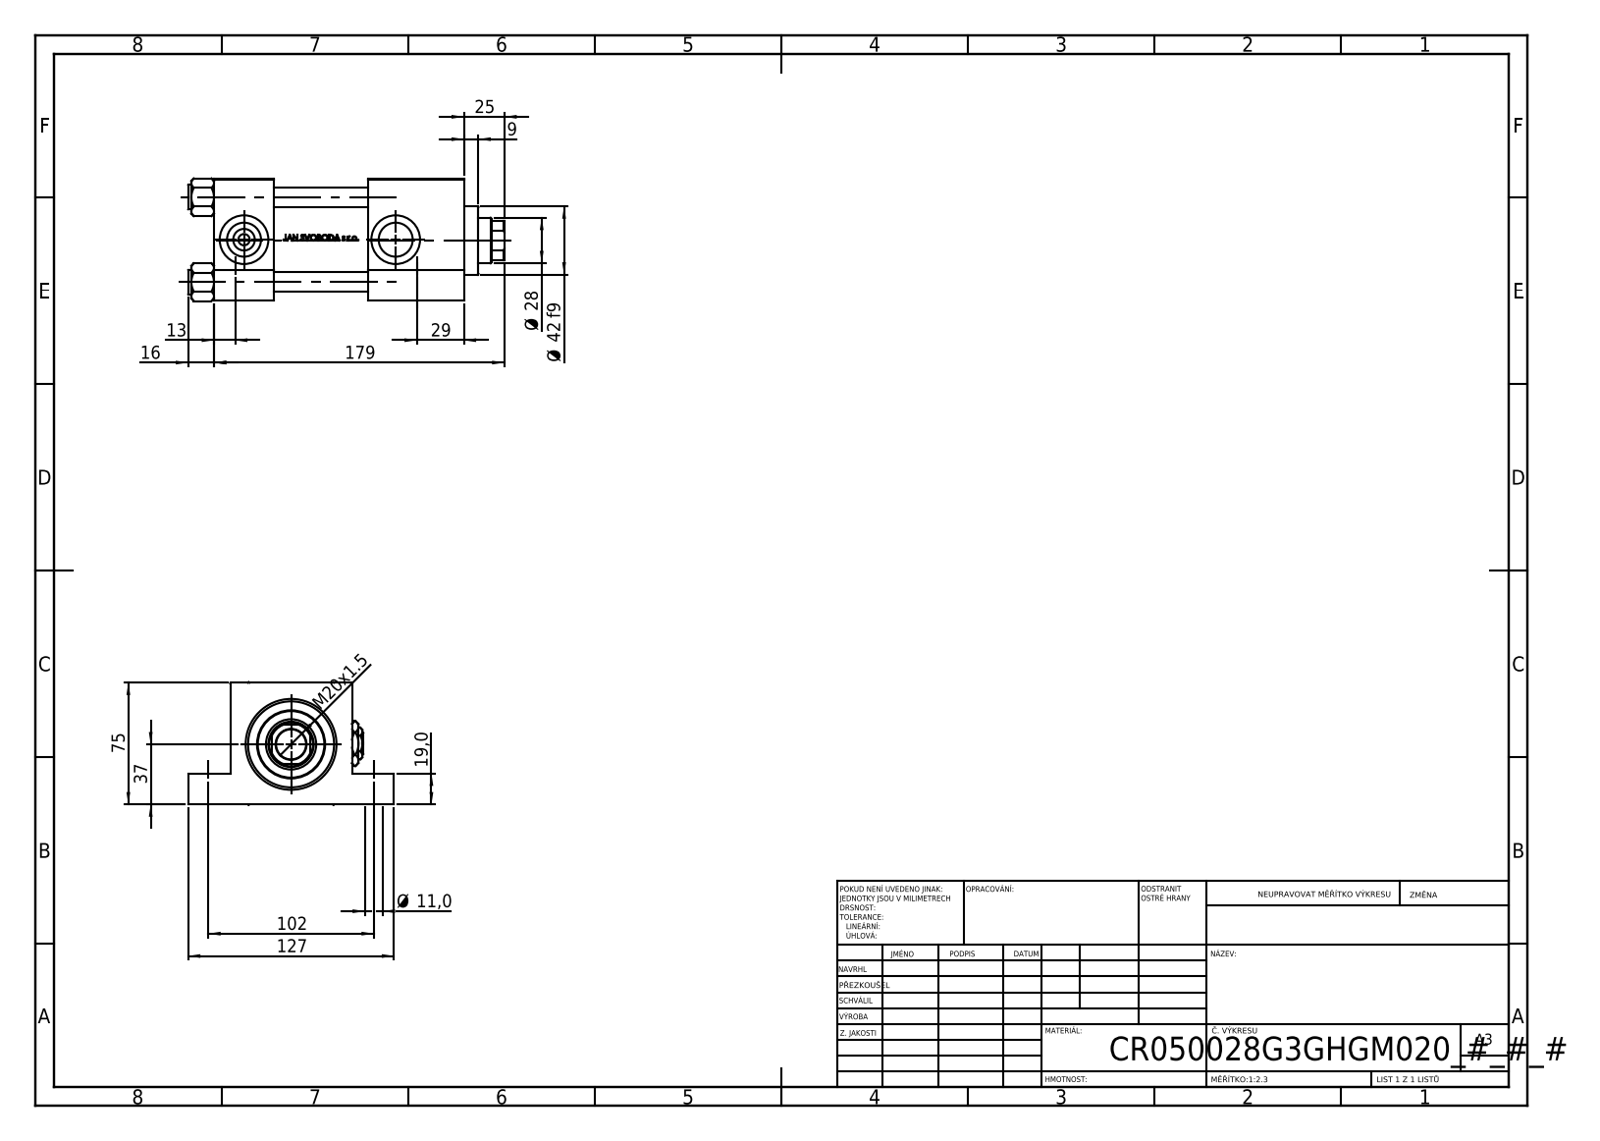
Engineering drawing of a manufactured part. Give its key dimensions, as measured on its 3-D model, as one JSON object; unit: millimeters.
{"part_name": "V215_VC_A; V215CR_VCP_G; Zatka_pro_OIL_PORT; V215CR_G_TYCINKA (+2 more)", "step_written_by": "SolidWorks 2019 (CONFIG_CONTROL_DESIGN)", "units": "millimeters", "bodies": {"solids": 13, "faces": 1183, "planar": 477, "cylindrical": 132, "other": 574}, "overall_size": [195, 127, 75.54], "volume_mm3": 762343, "surface_area_mm2": 167563, "round_holes": [[12, 4], [11, 3], [7, 2], [20.96, 2], [30, 2], [11, 1], [18.5, 1], [28, 1], [31, 1], [41, 1], [50, 1], [53, 1]], "round_bosses_or_shafts": [[15, 4], [56, 1], [42, 1]], "partial_cylinders_radius": [[13.5, 1]], "face_to_face_distances": [75, 37, 154, 117, 19, 56, 95, 58, 59, 26], "hole_center_spacings": [52.3, 36.63, 37.34, 73.96, 102, 112, 151.49, 93.5]}
